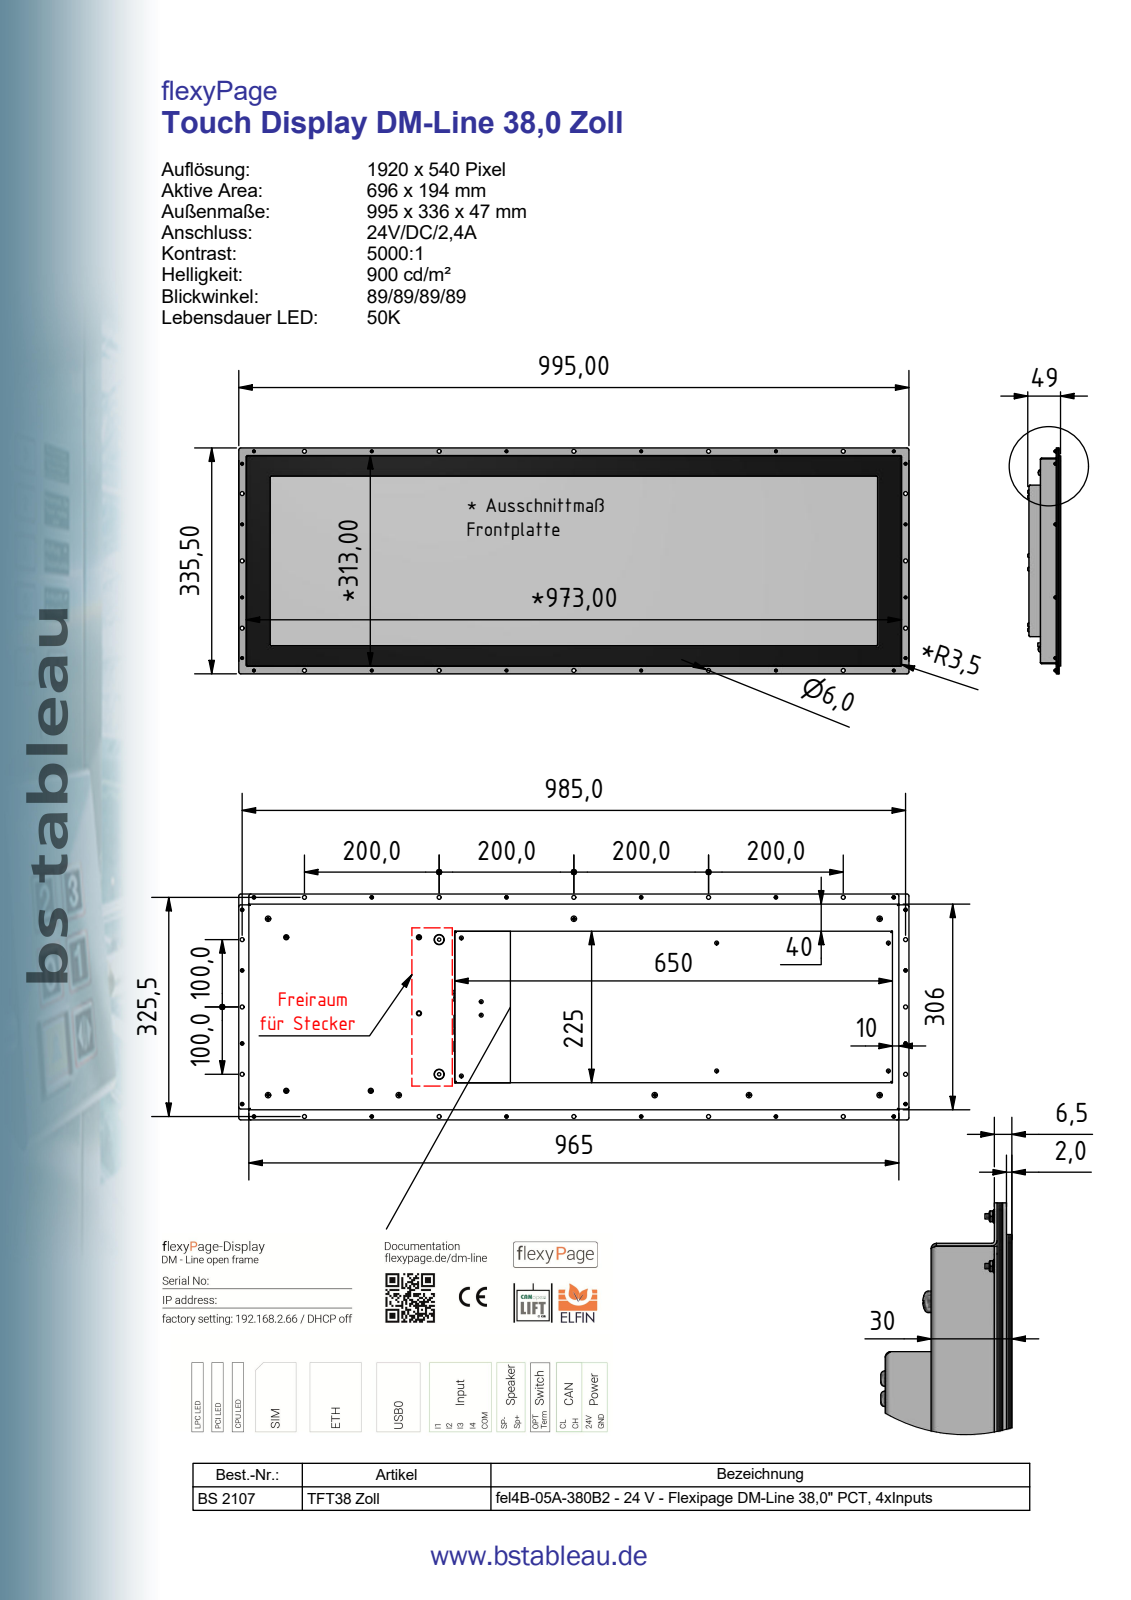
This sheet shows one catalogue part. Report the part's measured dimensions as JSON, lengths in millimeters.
{"part_name": "20000245 fel4B-05A-38,0 Zoll DM-Line; 00003620 fel4B-05A-38,0 Zoll DM-Line-UT; 00003600 TFT38 Zoll Strech Touch Rev.1.0-HB2; 00003601 TFT38 Zoll Strech Touch Rev.1.0-DB (+8 more)", "step_written_by": "Autodesk Inventor 2019 (AUTOMOTIVE_DESIGN)", "units": "millimeters", "bodies": {"solids": 122, "faces": 2789, "planar": 1614, "cylindrical": 588, "other": 587}, "overall_size": [995.04, 335.5, 48.65], "volume_mm3": 6487000, "surface_area_mm2": 2620000, "round_holes": [[2.46, 27], [1.57, 20], [2.2, 20], [6, 16], [5.41, 10], [3.24, 8], [4.2, 8], [7.5, 5], [3.2, 4], [3.45, 4], [3.6, 4], [4.92, 4]], "round_bosses_or_shafts": [[5, 20], [3.8, 20], [2, 20], [5.7, 14], [3, 14], [5.42, 12], [0.4, 11], [8, 8]], "partial_cylinders_radius": [[2, 51], [0.3, 21], [1, 20], [1.5, 18], [3, 12], [0.6, 9], [0.2, 8], [0.5, 6]], "face_to_face_distances": [1, 23, 3.5, 17, 29, 25.5, 30, 23.9, 26.5, 19.5], "hole_center_spacings": [100, 200, 382.03, 400, 340.51, 515.7, 300, 325.5]}
